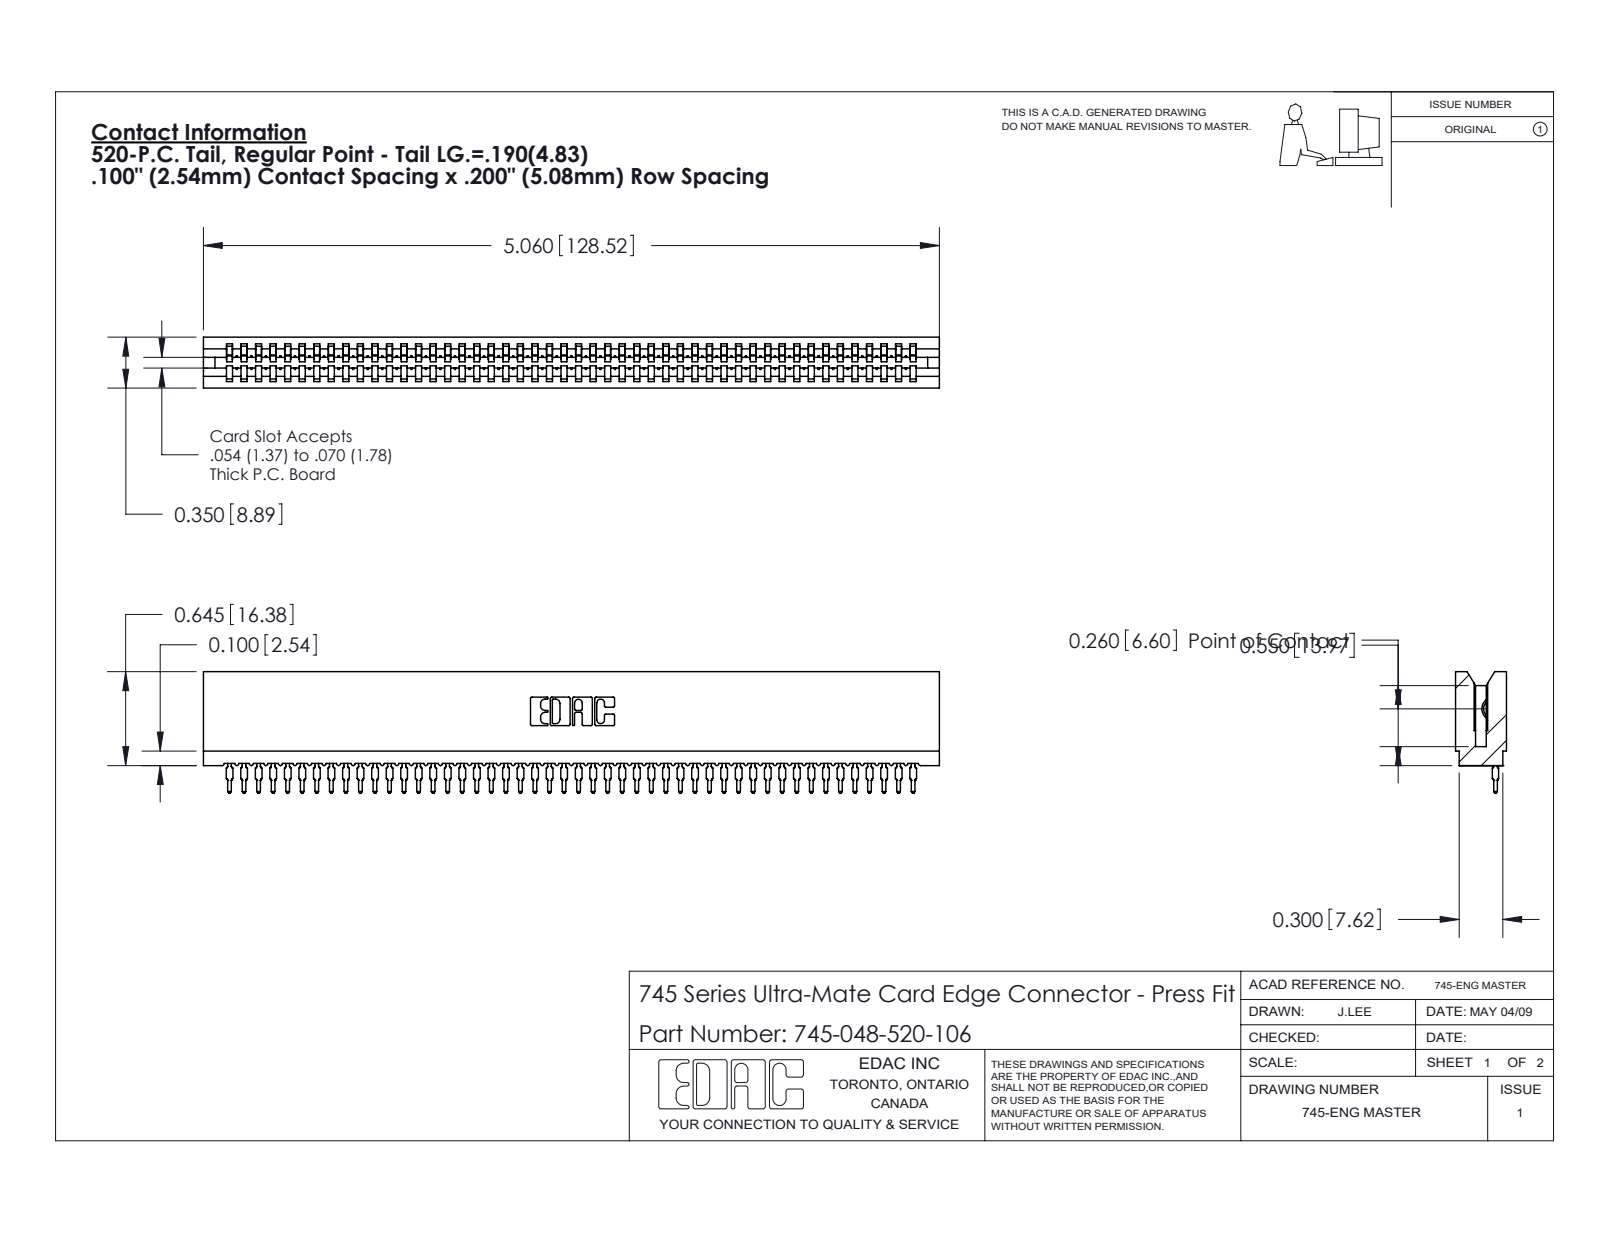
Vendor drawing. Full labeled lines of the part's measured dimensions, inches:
Part name (STEP PRODUCT): 745-048-520-106; 745-292-001_520; 745 Part_Insulator Option - 06
STEP written by: SolidWorks 2020 (CONFIG_CONTROL_DESIGN)
Units: inches
Bodies: 49 solids, 5472 faces (3272 planar, 952 cylindrical, 1248 other)
Overall size (bounding box): 5.06 × 0.836 × 0.35
Volume: 0.672 in³ · Surface area: 31.57 in²
Partial cylindrical surfaces — rounded edges, fillets, slot ends (radius × count): R0.015 ×96, R0.021 ×96, R0.01 ×22, R0.007 ×6, R0.031 ×6, R0.005 ×4, R0.011 ×4, R0.026 ×3
Main face-to-face distances: 0.35, 0.045, 0.305, 0.138, 0.212, 0.093, 0.167, 0.063, 0.287, 0.243
